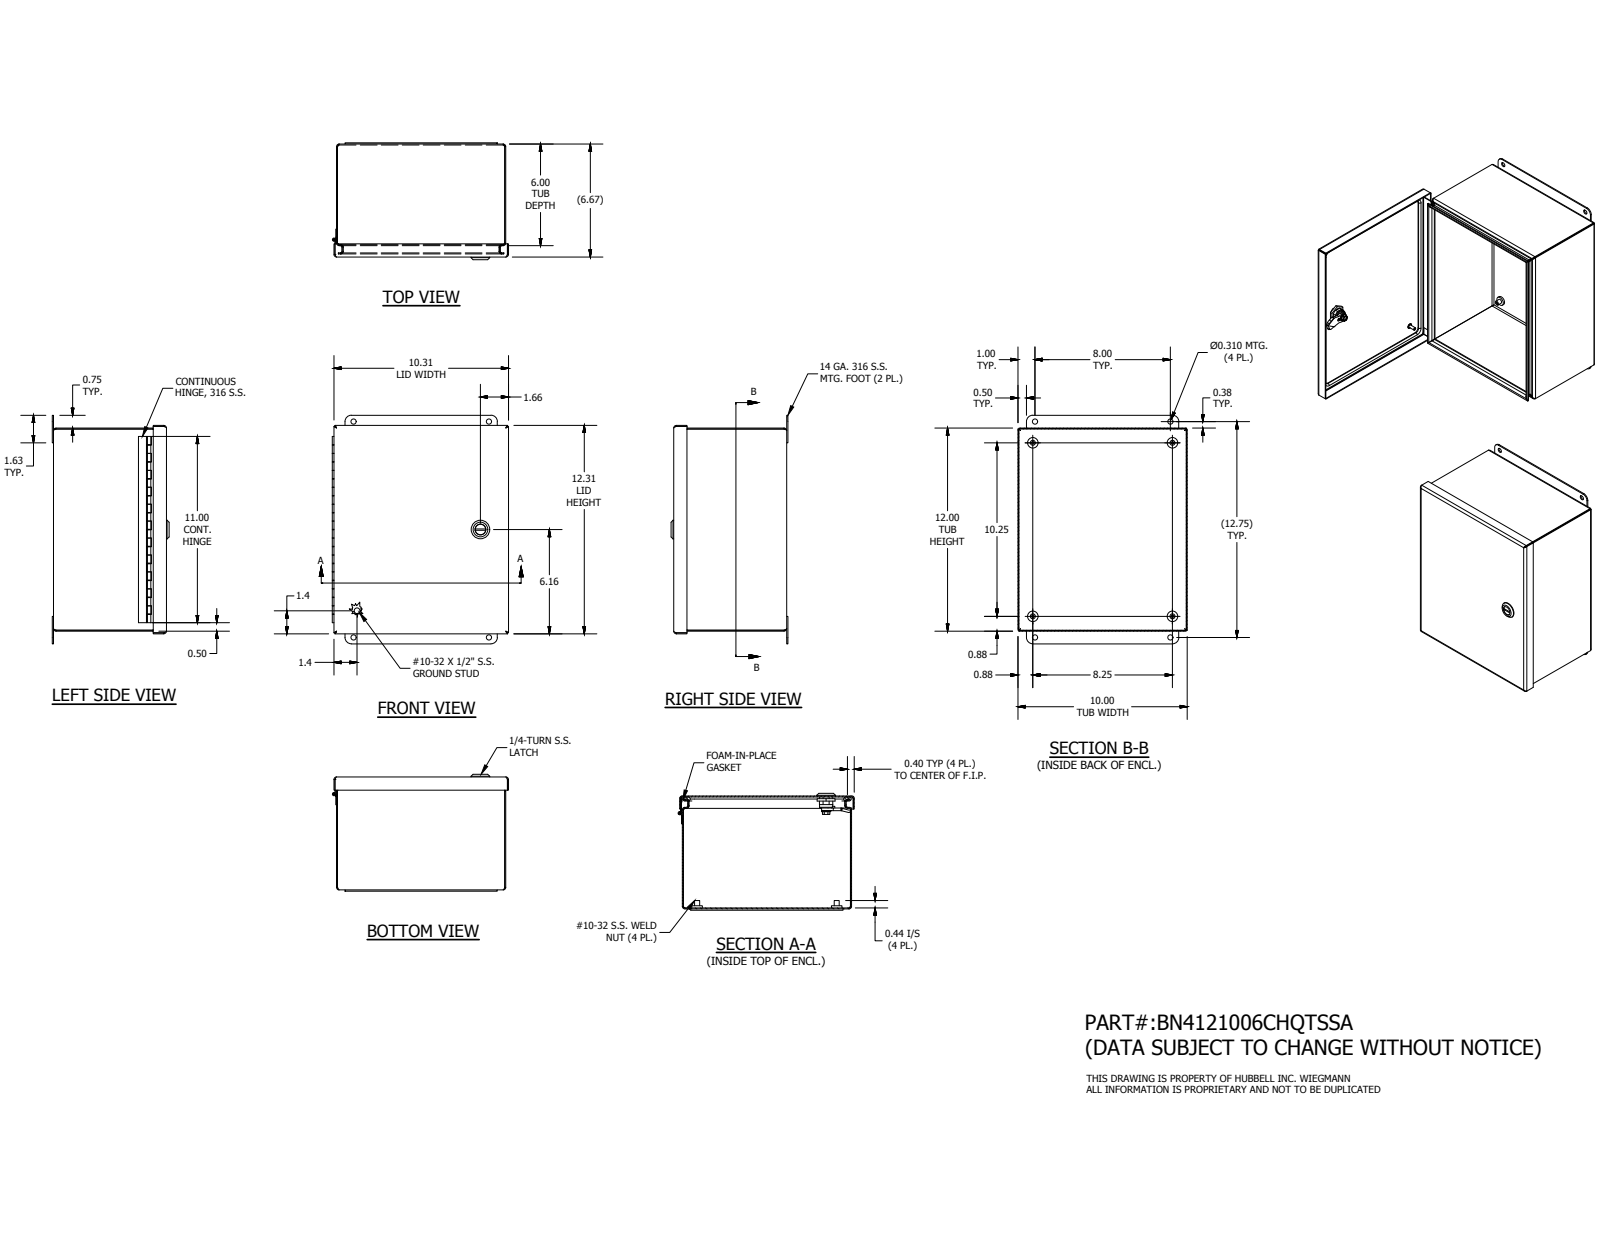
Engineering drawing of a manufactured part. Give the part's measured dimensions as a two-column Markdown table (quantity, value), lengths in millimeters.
| quantity | value |
| --- | --- |
| part name | BN41210CHQTSSALID; 12x10; 348130; 32884LH (+8 more) |
| STEP written by | Autodesk Inventor 2016 (AUTOMOTIVE_DESIGN) |
| units | millimeters |
| bodies | 21 solids, 671 faces (366 planar, 208 cylindrical, 97 other) |
| overall size | 342.9 × 264.46 × 175.39 |
| volume | 678 588 mm³ |
| surface area | 851 554 mm² |
| round holes (diameter × count) | 3.96 × 4, 7.87 × 4, 2.96 × 1, 5 × 1, 8 × 1, 10 × 1, 10.2 × 1, 16.1 × 1, 20.38 × 1 |
| round bosses / shafts (diameter × count) | 15.88 × 4, 7.62 × 4, 28 × 1, 19.8 × 1, 16 × 1, 15.2 × 1, 13.5 × 1, 12.8 × 1 |
| partial cylindrical surfaces (radius × count) | 2.38 × 20, 3.88 × 20, 3.17 × 16, 0.5 × 8, 4 × 4, 9.53 × 4, 2.31 × 2, 6.45 × 1 |
| main face-to-face distances | 1.5, 1.49, 167.99, 169.48, 166.49, 167.98, 303.3, 252.51, 254, 251.01 |
| hole center spacings | 31.91, 292.12, 357.65, 131.14, 203.2, 208.8, 208.81, 209.55 |
